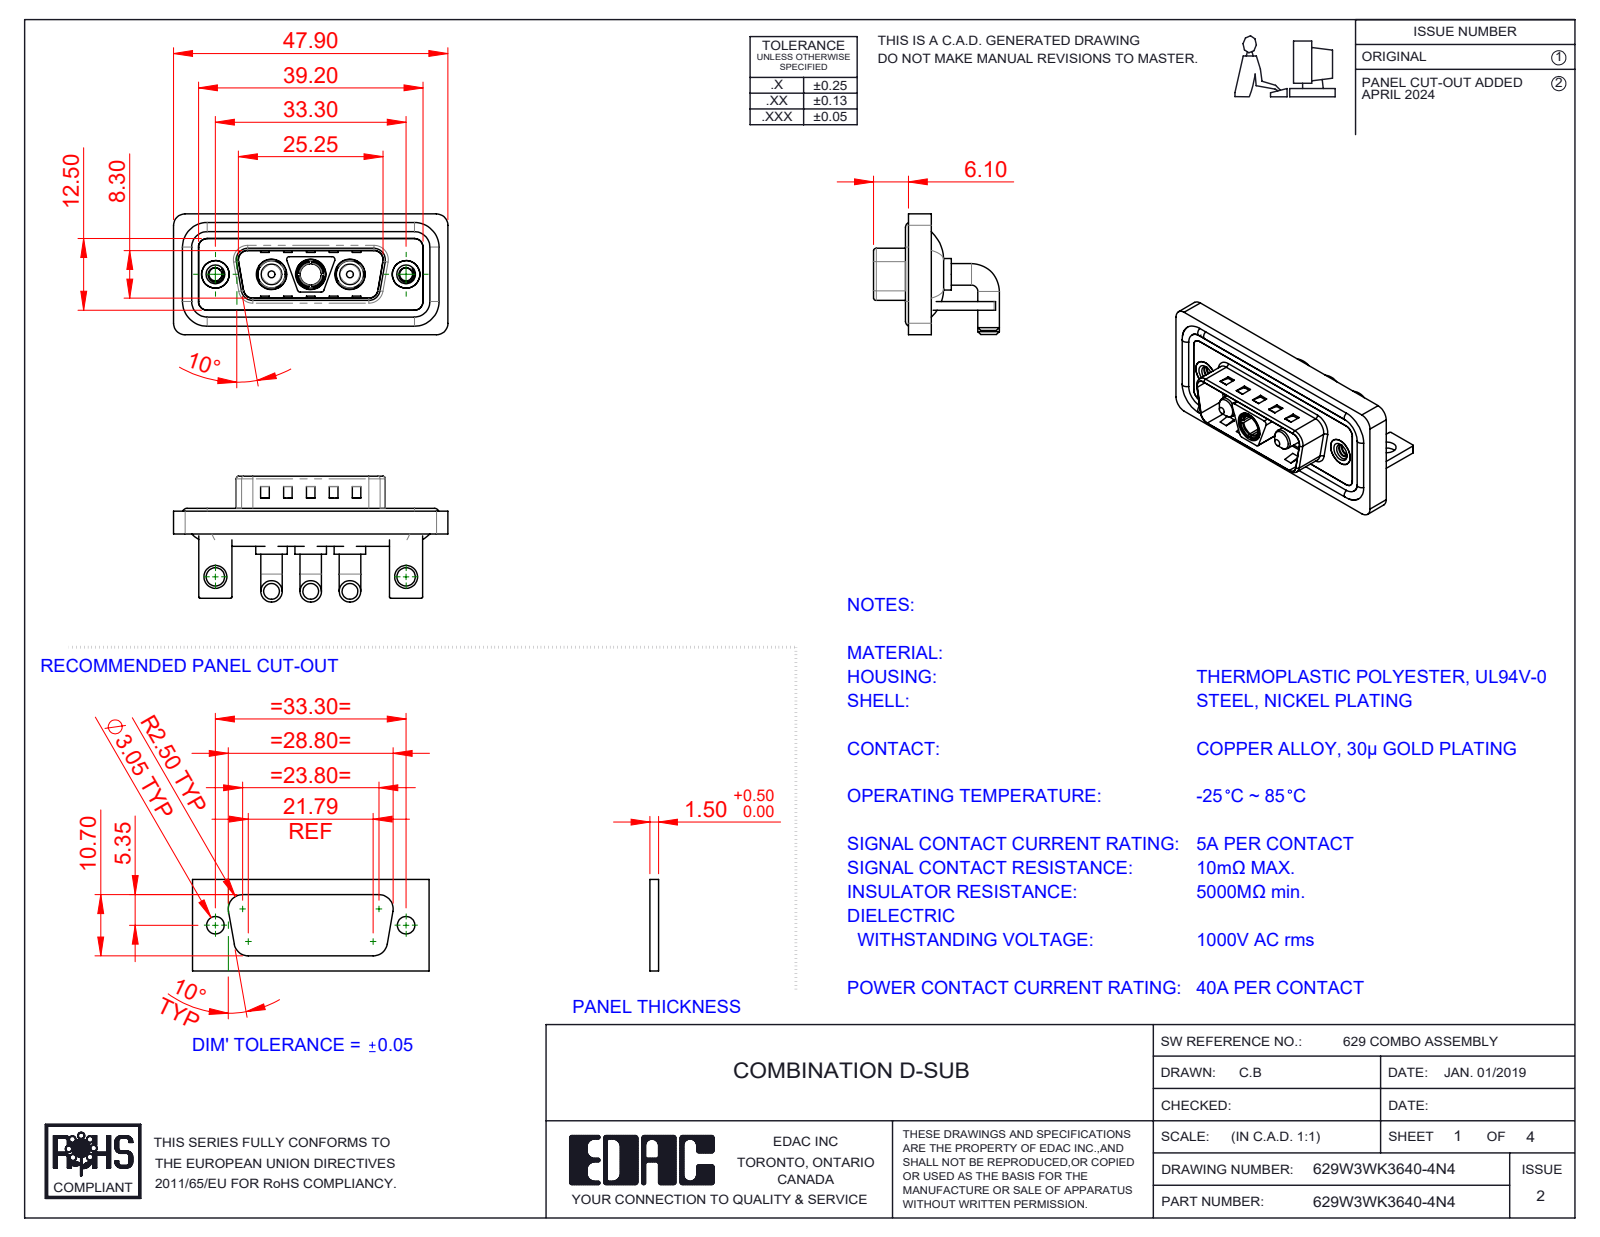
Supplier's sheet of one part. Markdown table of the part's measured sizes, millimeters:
| quantity | value |
| --- | --- |
| part name | Power Socket_40A RA; 629Combo Stabilizer Bracket; 629Combo Threaded Rivet_3; 629W3WK3640-4N4 (+5 more) |
| STEP written by | SolidWorks 2023 (CONFIG_CONTROL_DESIGN) |
| units | millimeters |
| bodies | 15 solids, 661 faces (251 planar, 274 cylindrical, 136 other) |
| overall size | 47.9 × 21.98 × 21.1 |
| volume | 6 385 mm³ |
| surface area | 10 136 mm² |
| round holes (diameter × count) | 4.85 × 3, 5.3 × 3, 2.26 × 2, 3.2 × 2, 4 × 2, 4.8 × 2, 5 × 2, 3.7 × 1 |
| round bosses / shafts (diameter × count) | 3.75 × 6, 1.6 × 4, 5.5 × 3, 5.2 × 3, 4.75 × 3, 4.9 × 2, 3.6 × 2, 4.96 × 1 |
| partial cylindrical surfaces (radius × count) | 2 × 21, 1.5 × 18, 0.25 × 16, 0.5 × 13, 1.6 × 8, 0.6 × 4, 0.65 × 4, 0.9 × 4 |
| main face-to-face distances | 0.4, 1.5, 0.8, 2.9, 1.1, 2.1, 3.7, 1.6, 1.2, 4.5 |
| hole center spacings | 6.85, 9.8, 16.65, 23.5, 33.3, 13.7 |
